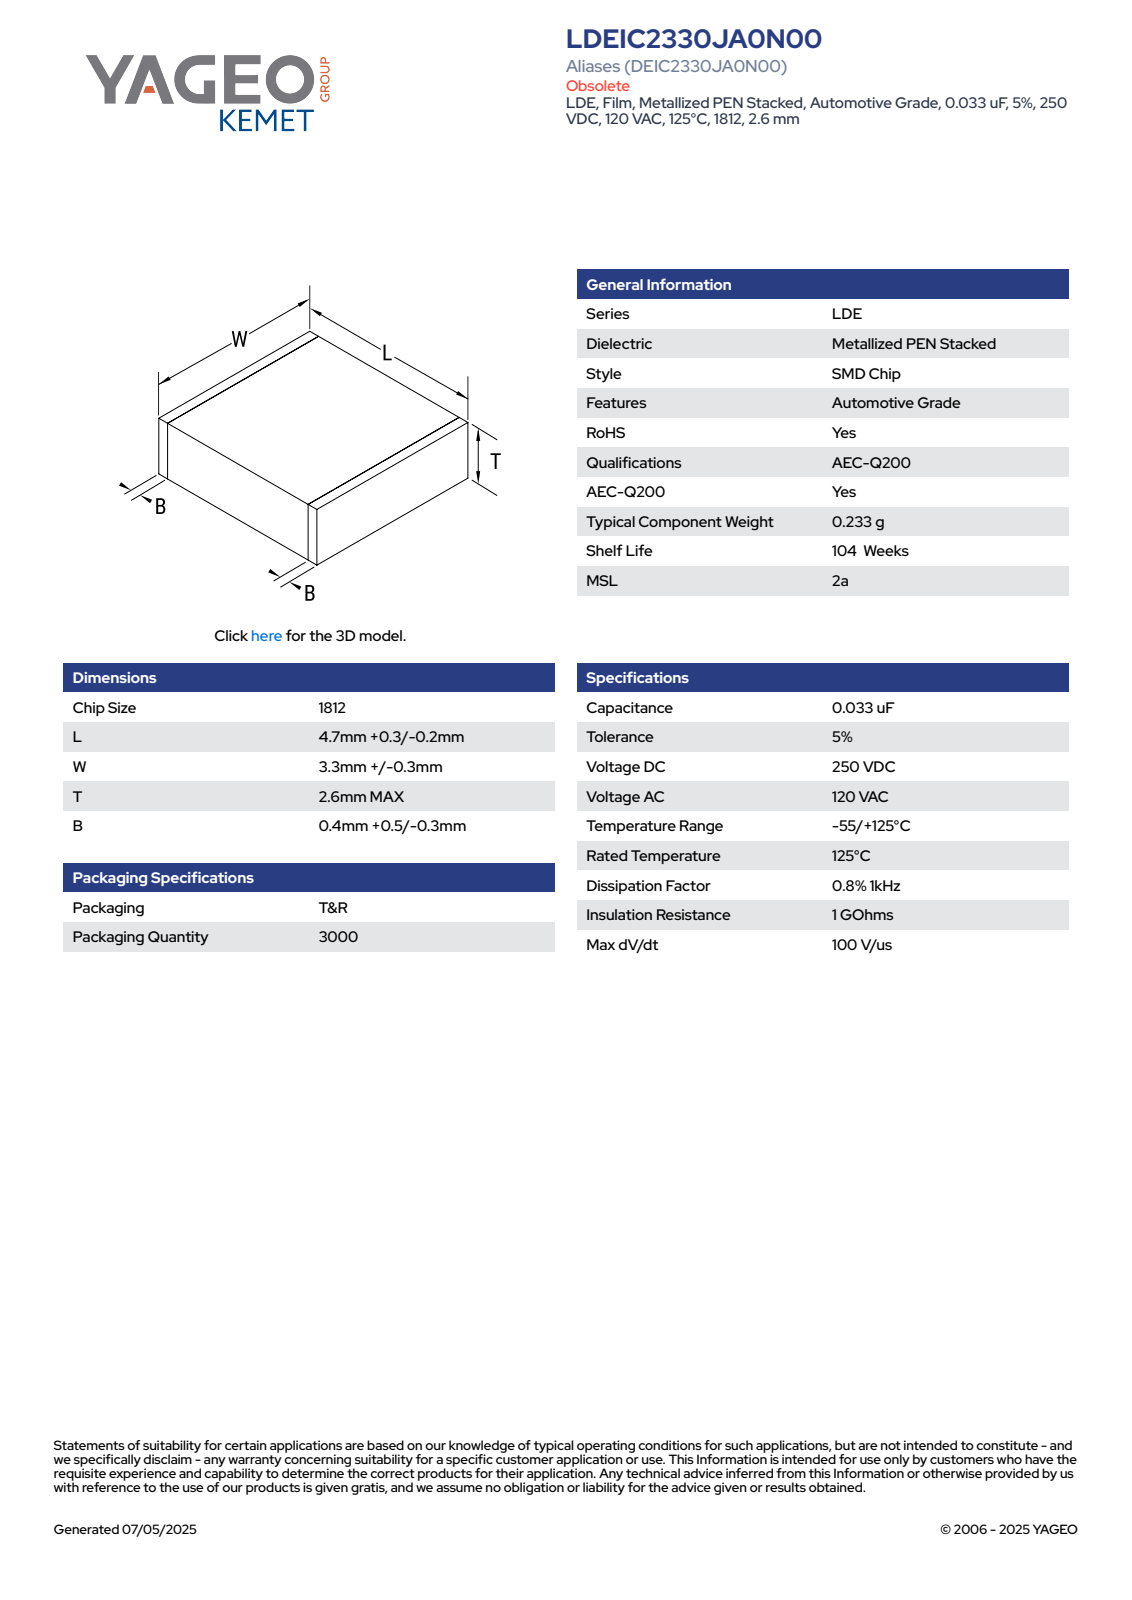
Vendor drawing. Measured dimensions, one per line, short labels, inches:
name: CFS_LDELDB_1812_L5W3.6T2.6B0.9
written by: SolidWorks 2020 (AUTOMOTIVE_DESIGN)
unit: in
bodies: 4 solids, 73 faces (73 planar, 0 cylindrical, 0 other)
size: 0.197 × 0.142 × 0.102
volume: 0.003 in³; area: 0.13 in²
face distances: 0.102, 0.141, 0.197, 0.102, 0.141, 0.102, 0.142, 0.02, 0.177, 0.157
